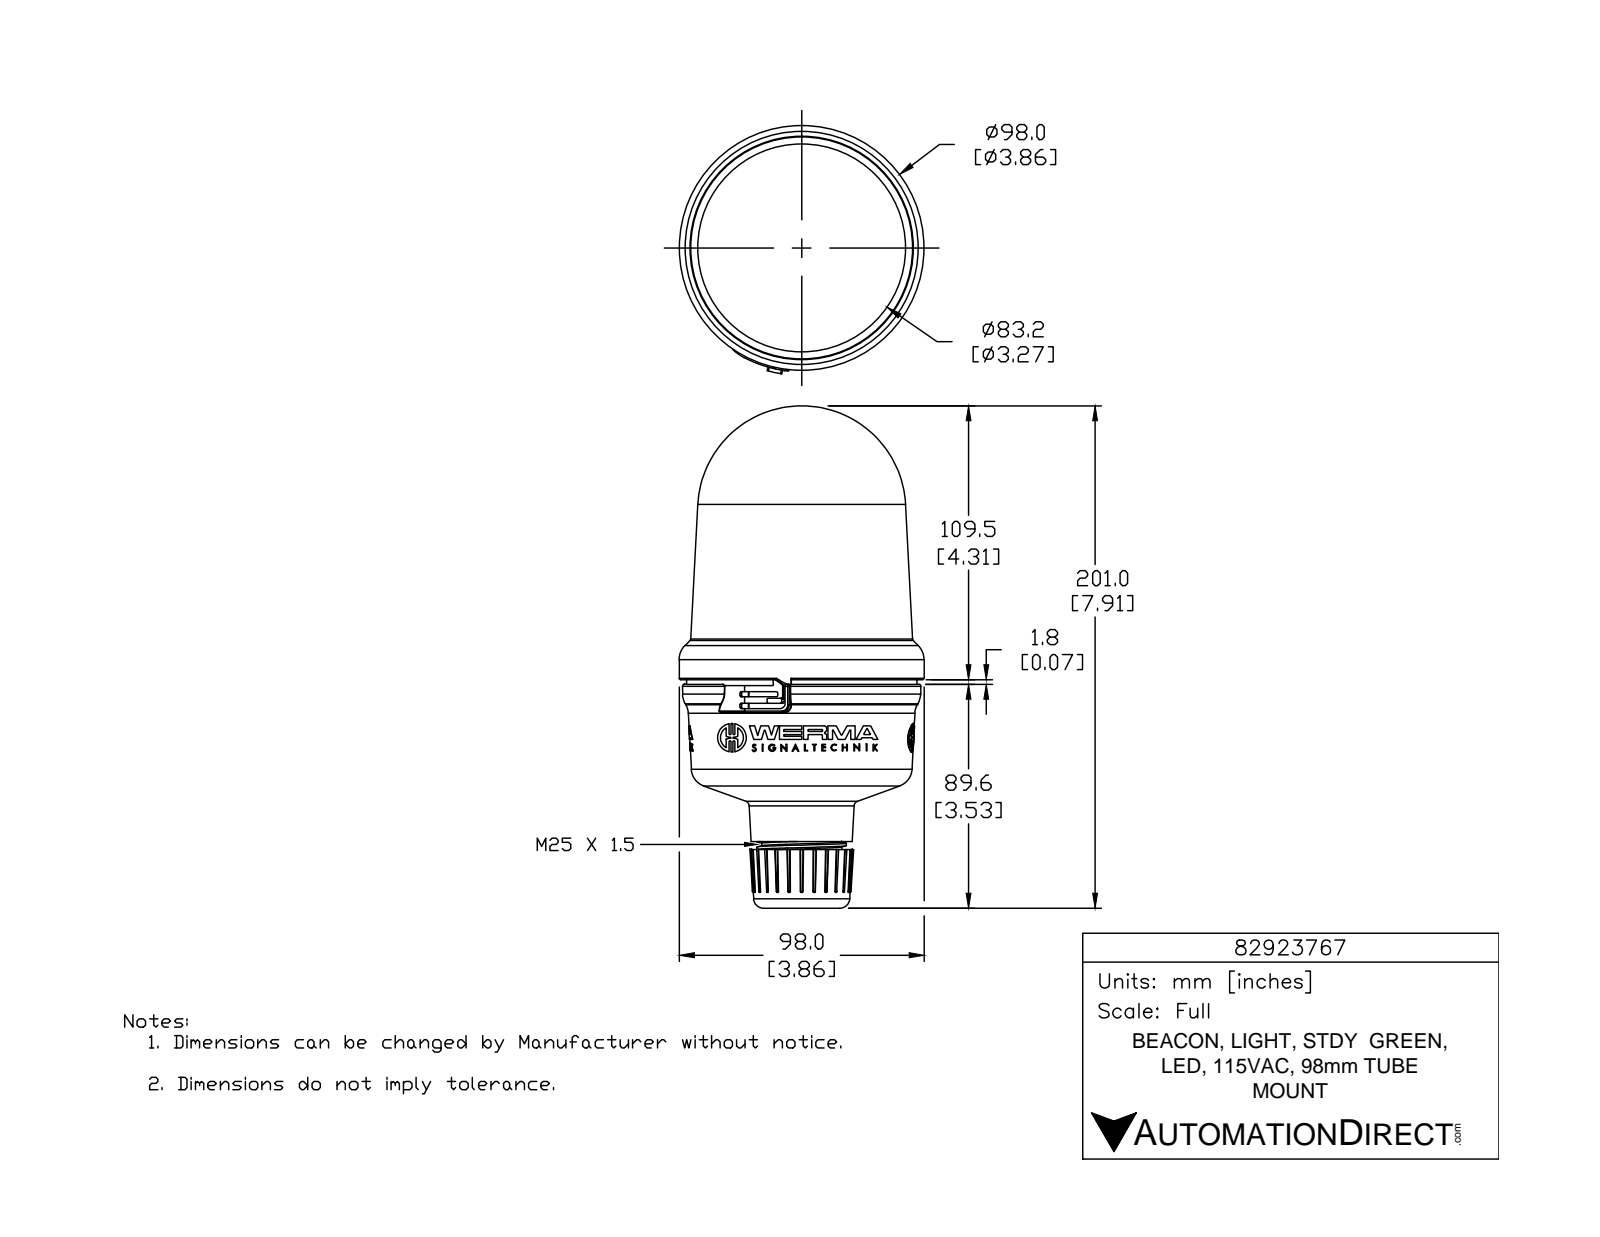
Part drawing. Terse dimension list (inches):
name: 82923767
written by: SolidWorks 2015 (AUTOMOTIVE_DESIGN)
unit: in
bodies: 1 solid, 1006 faces (554 planar, 189 cylindrical, 263 other)
size: 7.914 × 3.912 × 3.858
volume: 54.7 in³; area: 91.39 in²
holes: 3× ⌀0.078, 1× ⌀1.013, 1× ⌀1.024
bosses: 3× ⌀0.452, 3× ⌀0.113, 1× ⌀3.858, 1× ⌀1.409, 1× ⌀1.261
rounds: 12× R0.02, 9× R0.007, 6× R0.007, 6× R0.016, 6× R0.016, 6× R0.016, 6× R0.262, 3× R0.006
face distances: 2.214, 0.462, 2.676, 0.335, 0.127, 2.548, 2.603, 2.476, 2.141, 0.073
